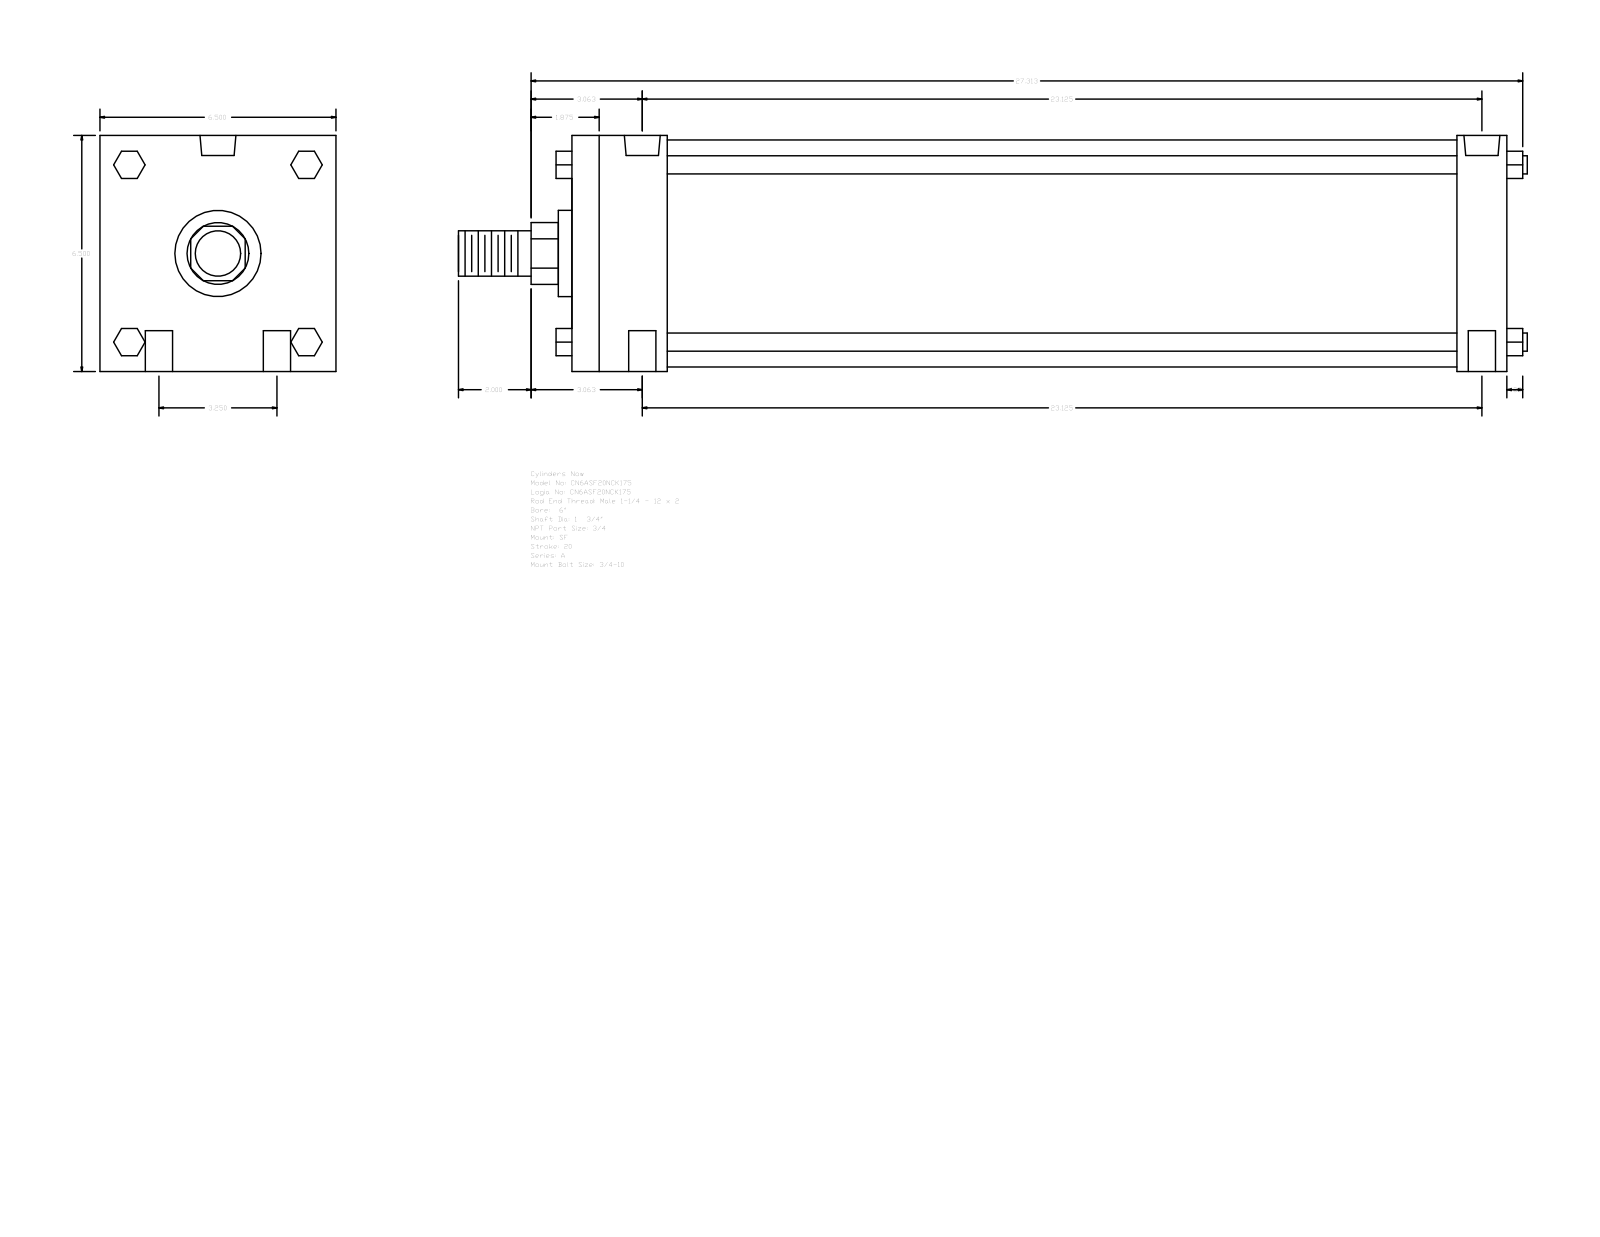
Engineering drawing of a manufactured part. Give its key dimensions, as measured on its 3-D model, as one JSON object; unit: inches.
{"part_name": "A_SF__0600_1.75", "step_written_by": "GSSL Pune (CONFIG_CONTROL_DESIGN)", "units": "inches", "bodies": {"solids": 0, "faces": 124, "planar": 94, "cylindrical": 30, "other": 0}, "overall_size": [29.437, 6.5, 6.5], "round_holes": [[0.75, 4], [0.594, 2], [0.989, 2]], "round_bosses_or_shafts": [[0.5, 4], [6.25, 1], [2.375, 1], [1.75, 1], [1.25, 1]], "partial_cylinders_radius": [[0.852, 1]], "face_to_face_distances": [6.5, 25.75, 2.625, 24.375, 1.375, 21.75, 23.125, 0.75, 2.44, 4.226], "hole_center_spacings": [1.625, 23.182, 23.125, 3.25, 23.352, 22.687]}
